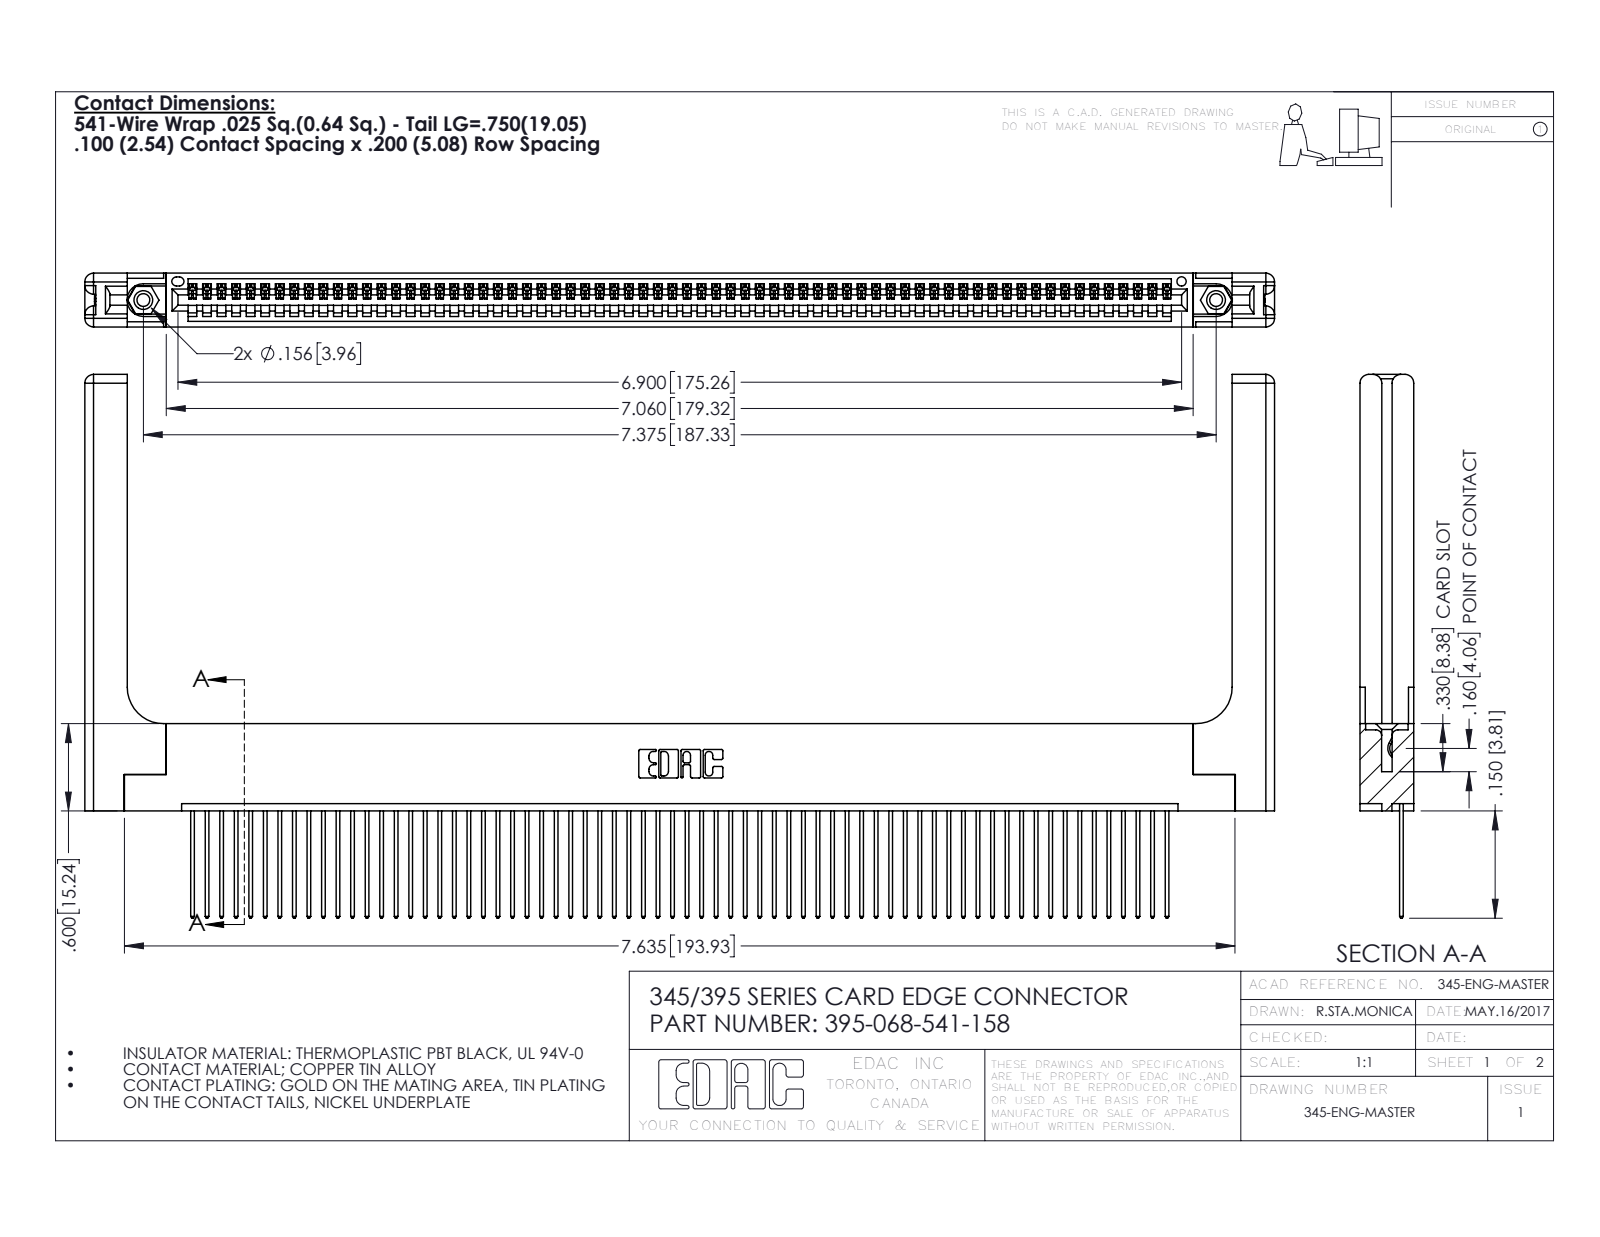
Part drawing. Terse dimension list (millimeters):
name: 345-250-001_345-250-001-102; 395-068-541-158; 345 Part_Flush Mounting Lugs - 0.156 Dia-TH; 345-220-058_345-220-058 (+1 more)
written by: SolidWorks 2016 (CONFIG_CONTROL_DESIGN)
unit: mm
bodies: 73 solids, 4326 faces (2948 planar, 1318 cylindrical, 60 other)
size: 207.7 × 94.9 × 9.4
volume: 28 680 mm³; area: 33 780 mm²
holes: 2× ⌀2.3, 2× ⌀3.2, 2× ⌀4, 1× ⌀1.6
bosses: 2× ⌀3.9
rounds: 136× R0.2, 136× R0.3, 22× R0.3, 16× R1.5, 6× R0.2, 6× R0.8, 3× R0.7, 2× R0.8
face distances: 1.8, 7.6, 9.4, 2.5, 6.9, 0.6, 5.1, 5.7, 3.8, 3.8
hole spacings: 6.9, 181.3, 187.3
